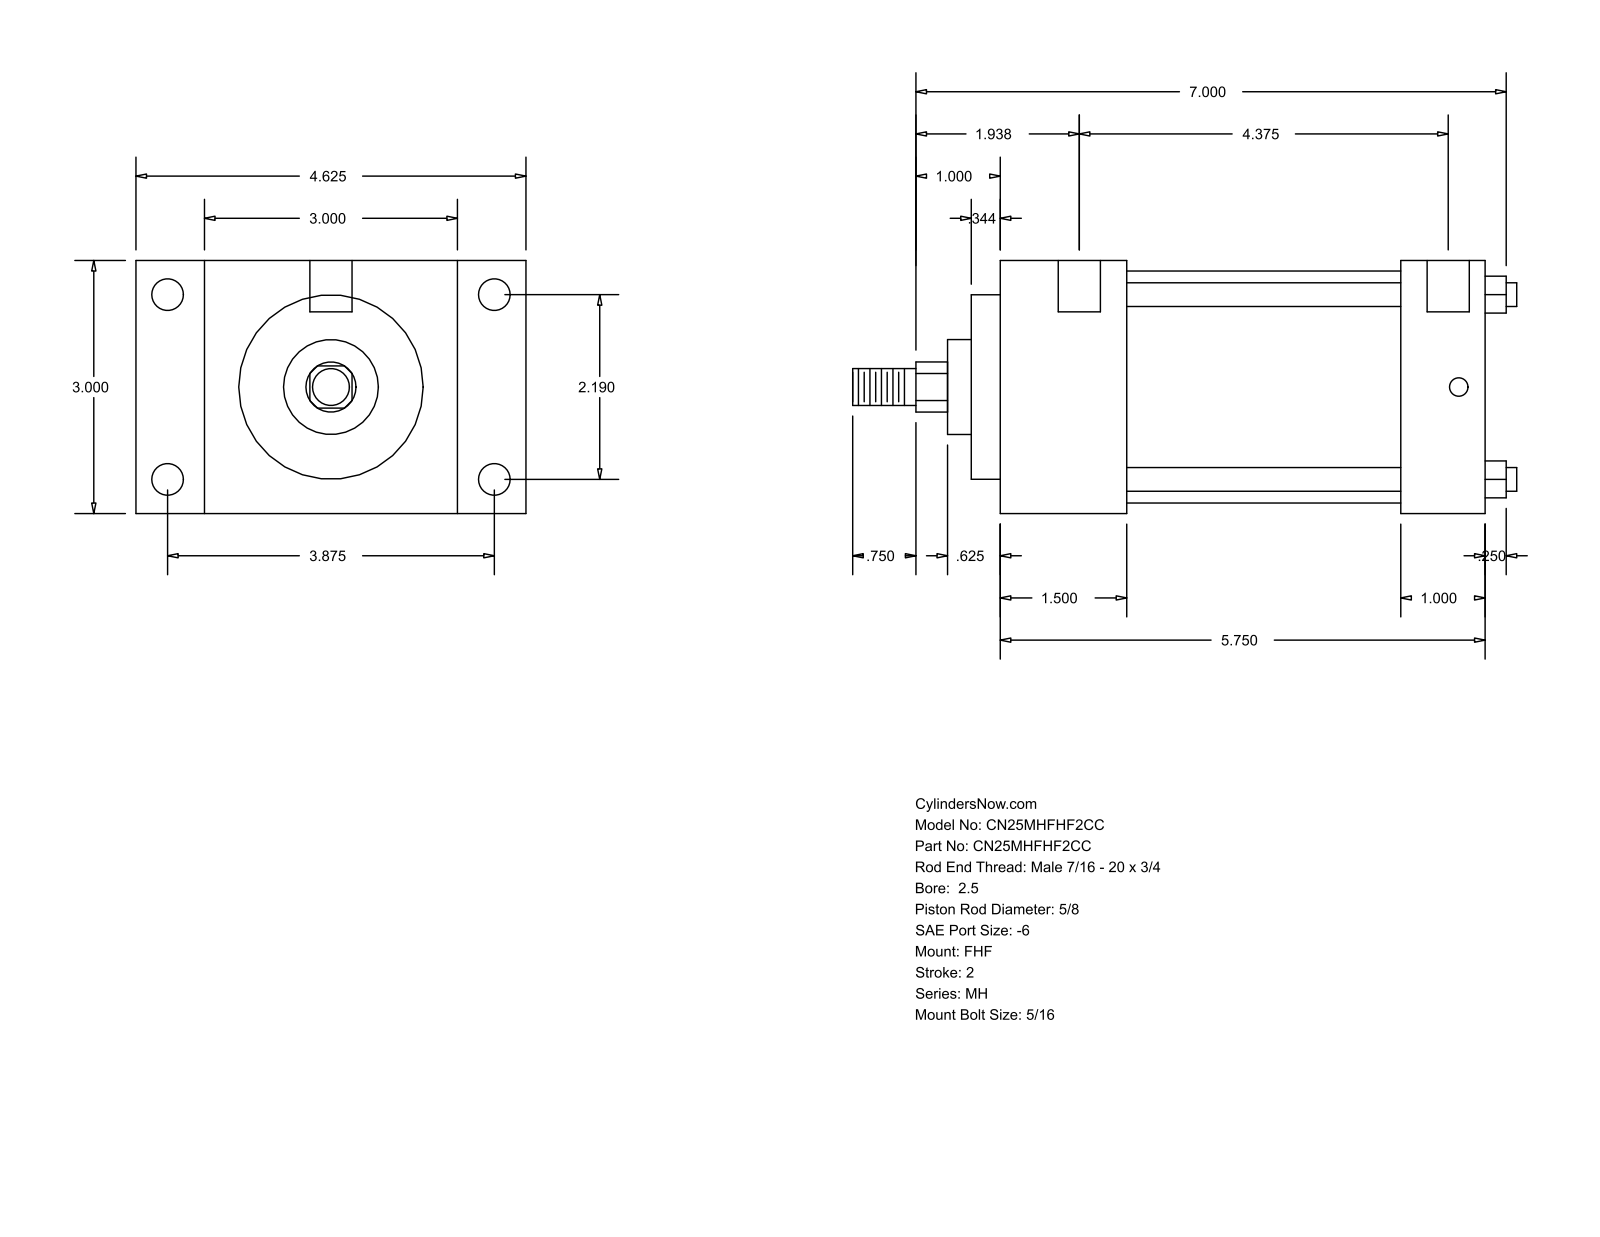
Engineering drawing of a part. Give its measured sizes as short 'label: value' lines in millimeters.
name: MH_FHF__0250_0.625
written by: GSSL Pune (CONFIG_CONTROL_DESIGN)
unit: mm
bodies: 0 solids, 90 faces (61 planar, 29 cylindrical, 0 other)
size: 200.03 × 117.47 × 76.2
holes: 4× ⌀5.56, 4× ⌀9.53, 2× ⌀12.7
bosses: 4× ⌀7.14, 1× ⌀69.85, 1× ⌀55.55, 1× ⌀28.57, 1× ⌀15.88, 1× ⌀11.11
rounds: 1× R7.54
face distances: 76.2, 146.05, 38.1, 107.95, 20.64, 96.84, 117.48, 25.4, 82.55, 120.65
hole spacings: 55.62, 98.42, 113.05, 119.06, 3.17, 4.76, 111.13, 114.3
